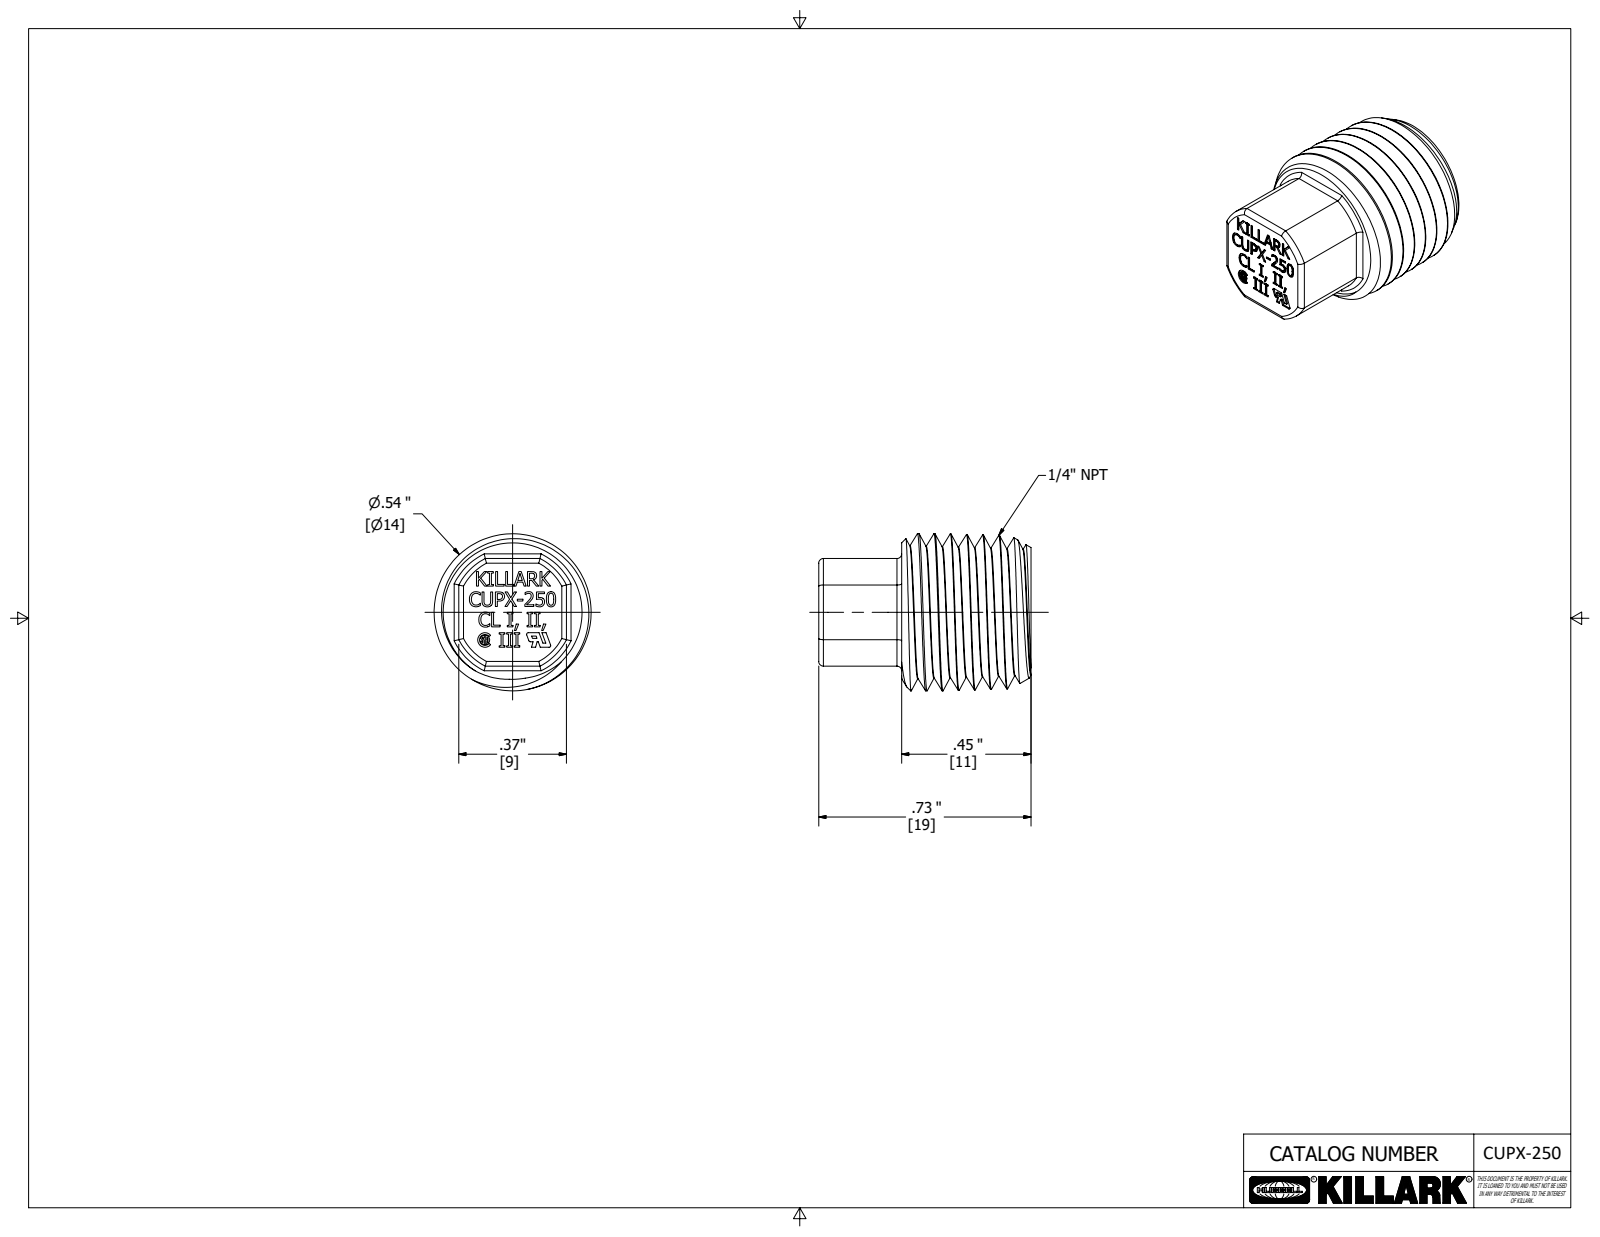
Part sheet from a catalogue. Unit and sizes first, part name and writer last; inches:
Units: inches
Overall size (bounding box): 0.73 × 0.54 × 0.54
Round bosses / shafts (diameter × count): ⌀0.54 ×1
Partial cylindrical surfaces — rounded edges, fillets, slot ends (radius × count): R0.016 ×8, R0.005 ×3, R0.011 ×1, R0.016 ×1, R0.019 ×1, R0.025 ×1, R0.207 ×1
Main face-to-face distances: 0.37, 0.73, 0.445, 0.285, 0.725, 0.28, 0.44, 0.72, 0.07, 0.05
Volume: 0.119 in³ · Surface area: 1.974 in²
Bodies: 1 solid, 500 faces (336 planar, 28 cylindrical, 136 other)
Part name (STEP PRODUCT): 12999
STEP written by: Autodesk Inventor 2020 (AUTOMOTIVE_DESIGN)
